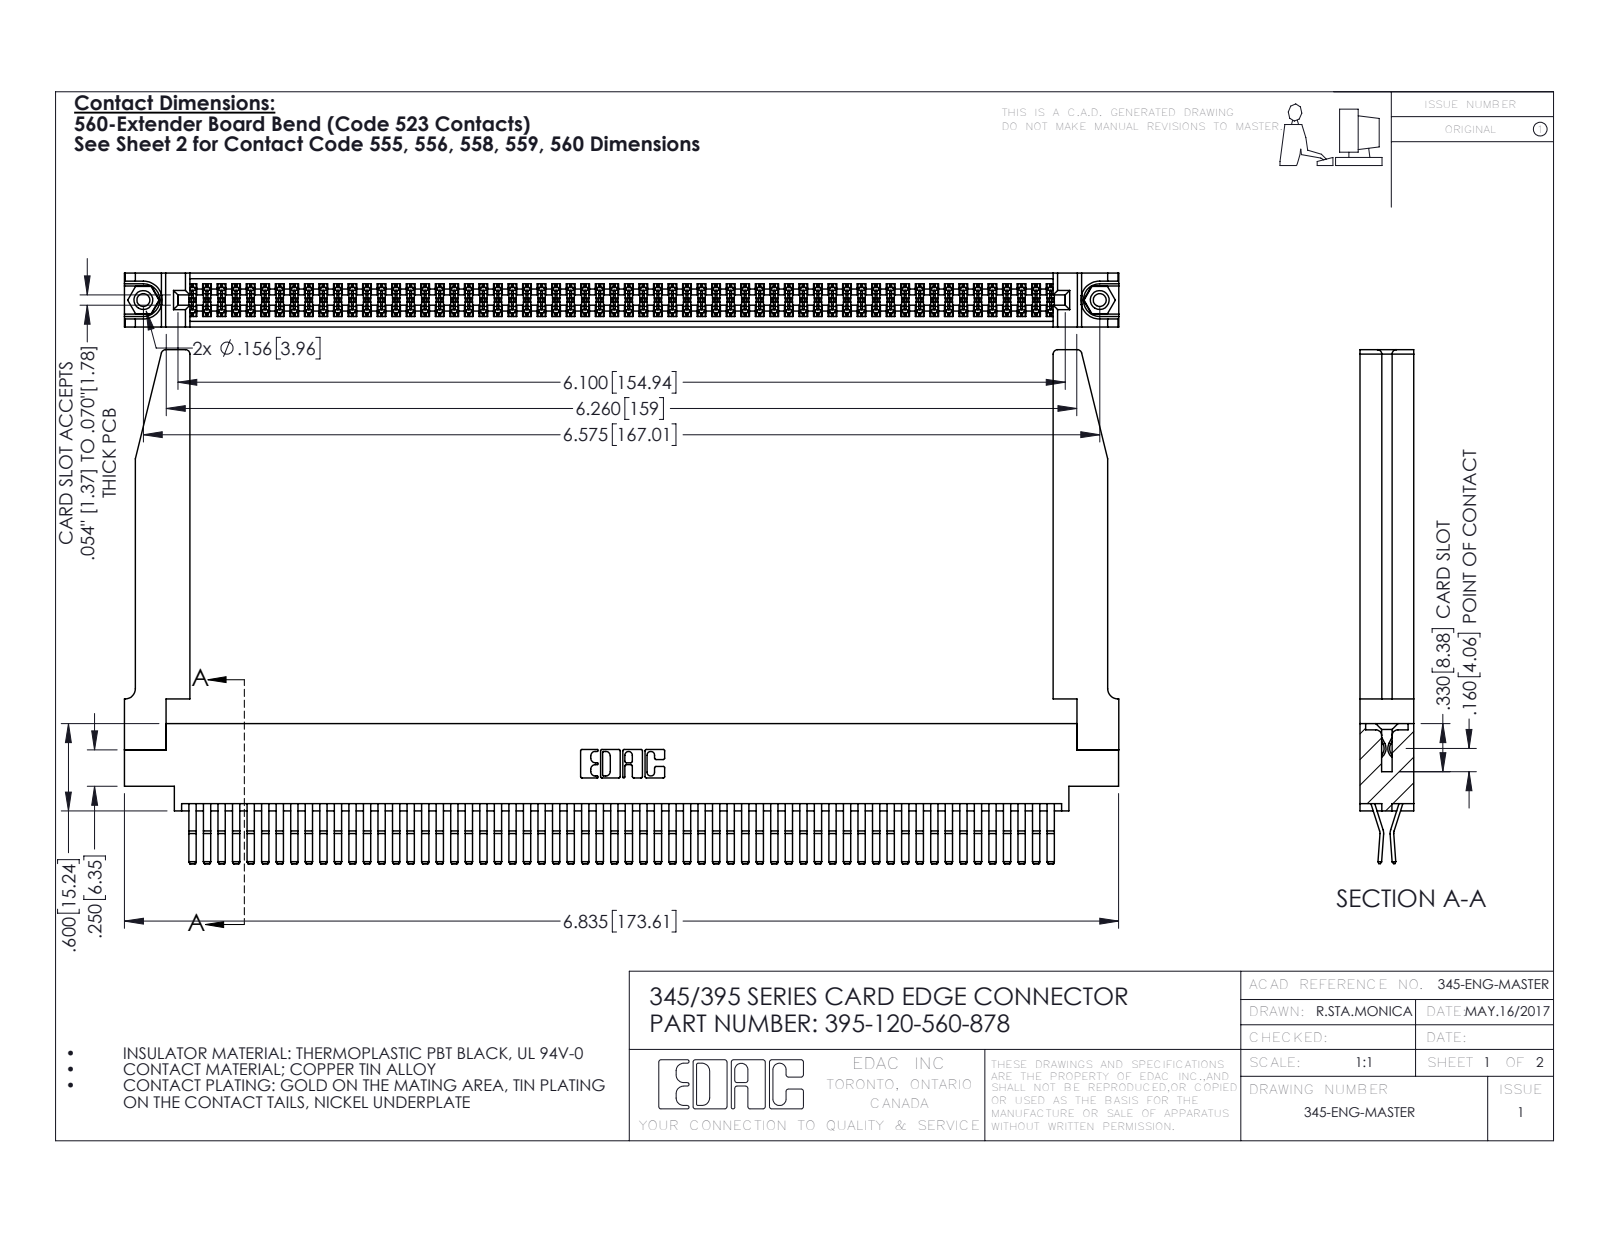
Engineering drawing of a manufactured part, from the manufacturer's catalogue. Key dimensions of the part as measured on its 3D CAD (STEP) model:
Part name (STEP PRODUCT): 395-120-560-878; 345-220-078_345-220-078; 345-292-001_560 Tail; 345 Part_0.170 Offset - 0.156 Dia-TH (+1 more)
STEP written by: SolidWorks 2016 (CONFIG_CONTROL_DESIGN)
Units: inches
Bodies: 125 solids, 6604 faces (4186 planar, 2366 cylindrical, 52 other)
Overall size (bounding box): 6.836 × 3.532 × 0.37
Volume: 1.555 in³ · Surface area: 55.07 in²
Round holes (diameter × count): ⌀0.089 ×2, ⌀0.125 ×2, ⌀0.156 ×2, ⌀0.064 ×1
Round bosses / shafts (diameter × count): ⌀0.155 ×2
Partial cylindrical surfaces — rounded edges, fillets, slot ends (radius × count): R0.006 ×180, R0.01 ×22, R0.03 ×8, R0.007 ×6, R0.031 ×6, R0.026 ×3, R0.01 ×2, R0.014 ×2
Main face-to-face distances: 0.072, 0.37, 0.298, 0.025, 0.098, 0.272, 0.2, 0.225, 0.175, 0.148
Hole centre spacings: 0.27, 6.339, 6.575
